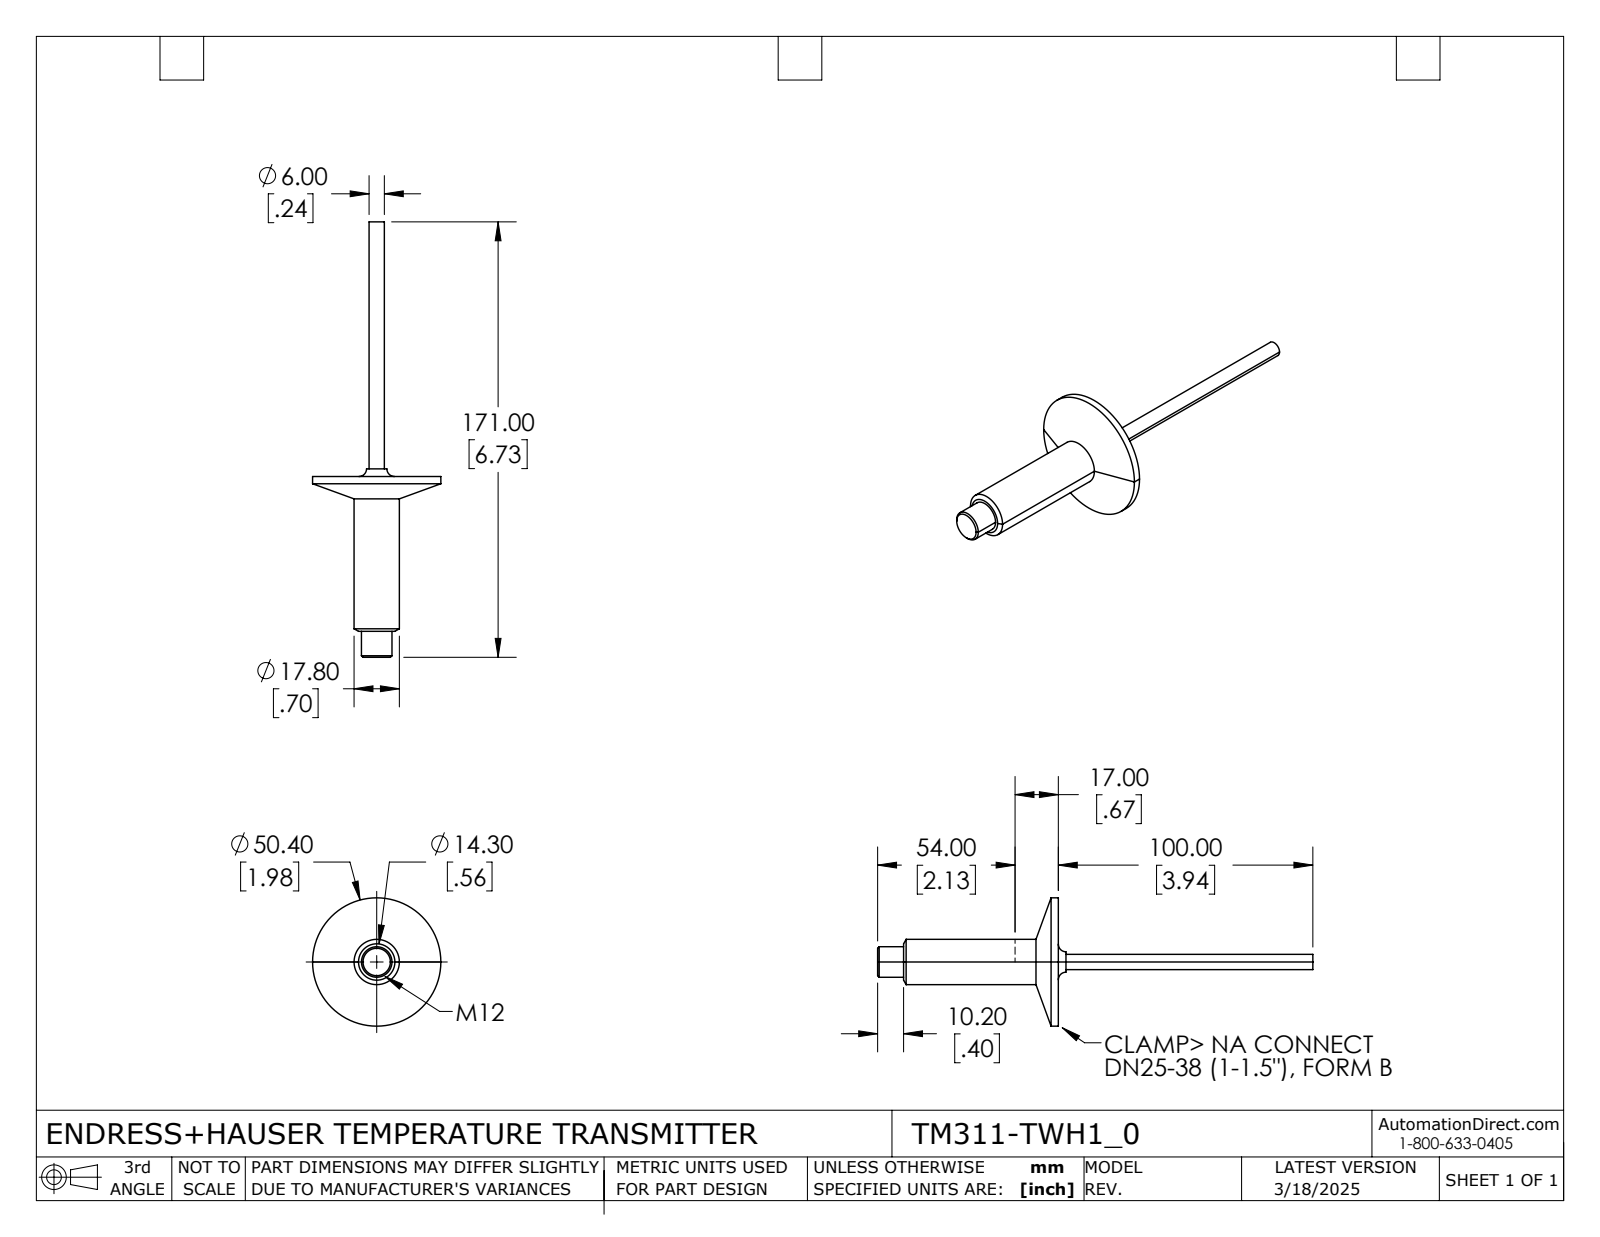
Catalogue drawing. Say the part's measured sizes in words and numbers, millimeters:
The part is named "TM311-TWH1_0". Its 3-D file was written by "SolidWorks 2021 (AUTOMOTIVE_DESIGN)". It is 1 solid with 29 faces: 6 planar, 8 cylindrical and 15 other. Overall it measures 171 by 50.4 by 50.4 millimeters. Its volume is 28 040 cubic millimeters and its surface area 9 903 square millimeters. Round bosses or shafts: 1 of diameter 50.4, 1 of diameter 17.8, 1 of diameter 12, 1 of diameter 6. The main face-to-face distances are 71, 60.8, 10.2, 100, 160.8, 171, 97, 3, 63.8, 74.
